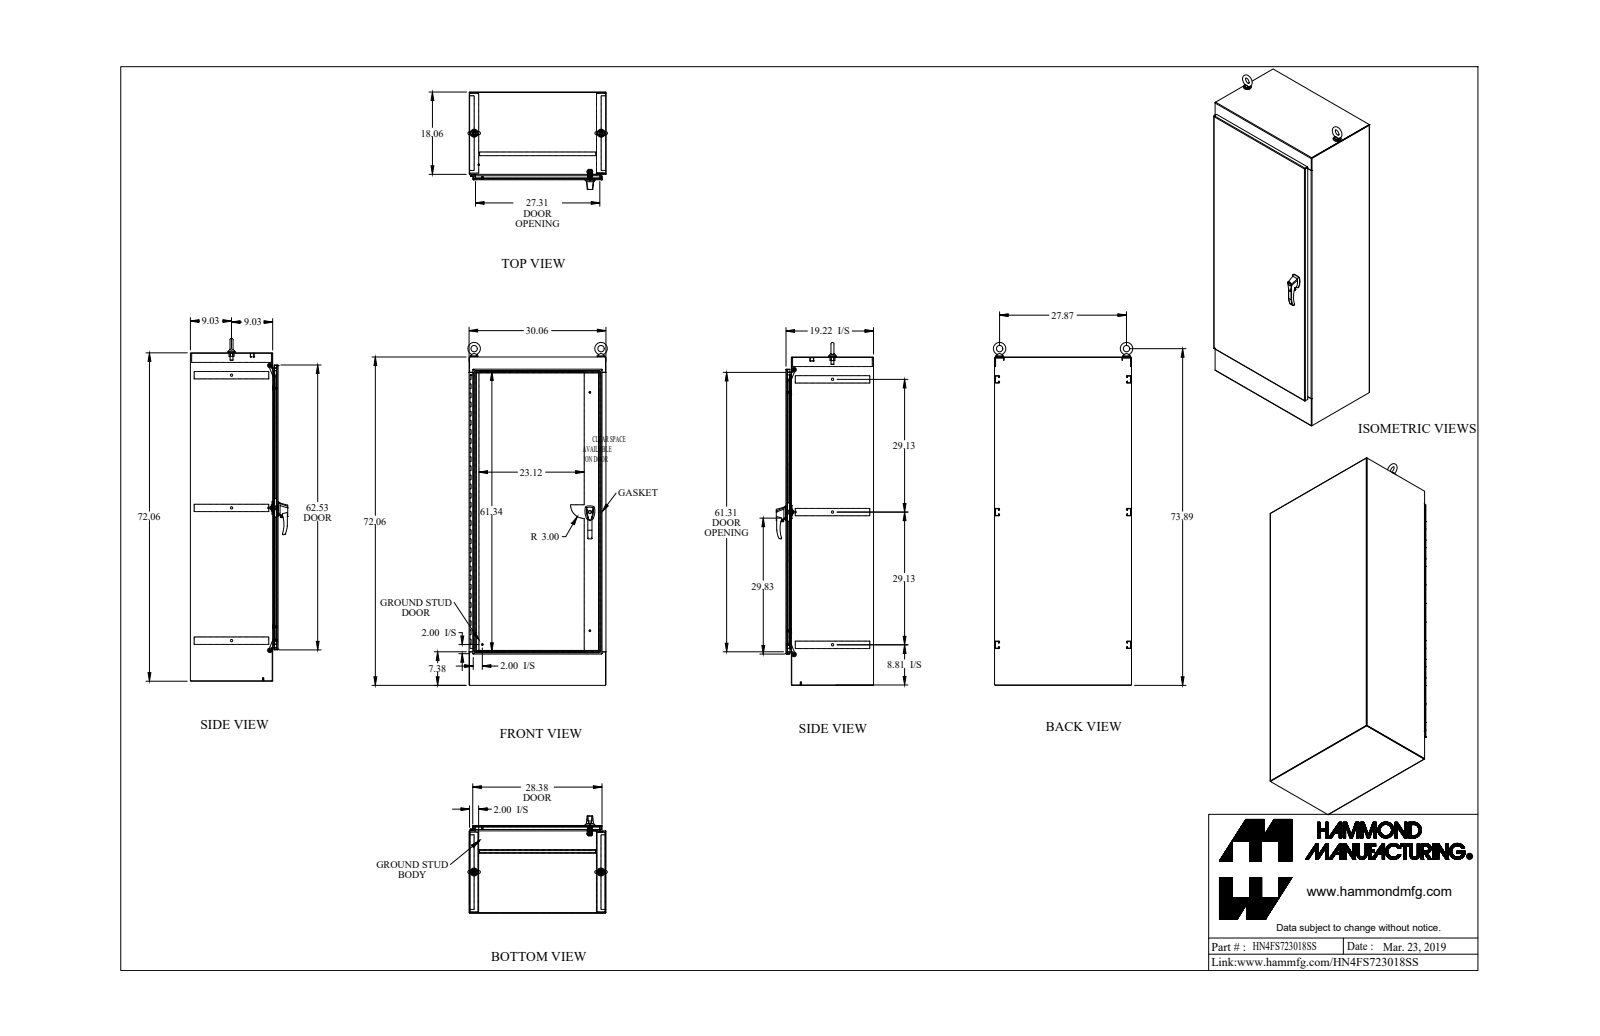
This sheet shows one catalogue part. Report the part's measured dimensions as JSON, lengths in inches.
{"part_name": "HN4FS723018SS", "step_written_by": "SolidWorks 2018 (AUTOMOTIVE_DESIGN)", "units": "inches", "bodies": {"solids": 52, "faces": 1857, "planar": 854, "cylindrical": 838, "other": 165}, "overall_size": [75.256, 30.604, 21.362], "volume_in3": 930.6, "surface_area_in2": 19540, "round_holes": [[0.304, 10], [0.35, 7], [0.5, 3], [0.25, 2], [0.257, 2], [0.28, 2], [0.281, 2], [0.313, 2], [0.39, 2], [0.413, 2], [0.527, 2], [0.625, 2]], "round_bosses_or_shafts": [[1.75, 2], [1.5, 2], [1.25, 2], [1, 2], [0.75, 2], [0.738, 2], [0.63, 2], [0.625, 2]], "partial_cylinders_radius": [[0.043, 42], [0.138, 36], [0.5, 23], [0.125, 22], [0.018, 16], [0.048, 15], [0.06, 15], [0.143, 15]], "face_to_face_distances": [0.095, 19.152, 29.965, 19.057, 19.247, 29.87, 30.06, 71.965, 17.965, 1.187], "hole_center_spacings": [6, 12, 18, 24, 30, 36, 42, 0.015]}
